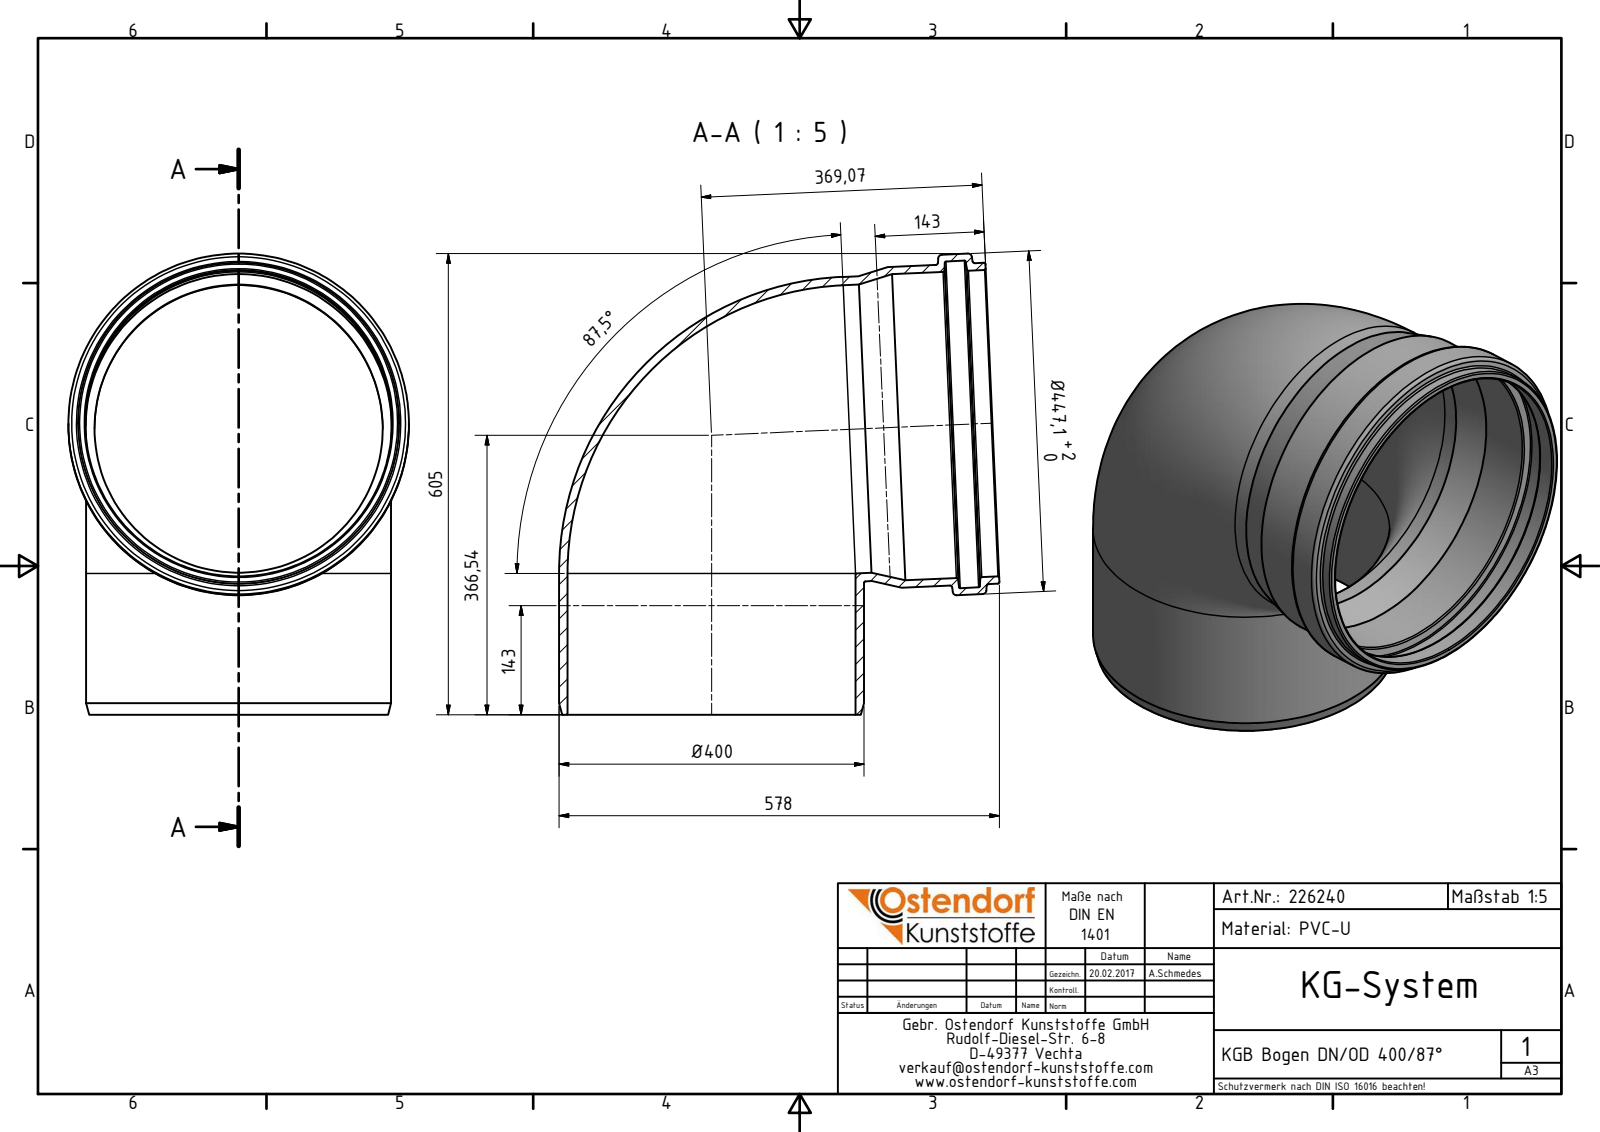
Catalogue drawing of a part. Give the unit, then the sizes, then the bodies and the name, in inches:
Units: inches
Overall size (bounding box): 23.819 × 22.756 × 17.602
Round holes (diameter × count): ⌀14.896 ×2, ⌀15.827 ×1, ⌀15.843 ×1, ⌀16.894 ×1
Round bosses / shafts (diameter × count): ⌀15.762 ×2, ⌀17.602 ×1, ⌀16.591 ×1, ⌀16.579 ×1
Volume: 475.4 in³ · Surface area: 2 672 in²
Bodies: 1 solid, 32 faces (2 planar, 10 cylindrical, 20 other)
Part name (STEP PRODUCT): 226240 KGB Bogen DN_OD 400_87°
STEP written by: Autodesk Inventor 2016 (AUTOMOTIVE_DESIGN)
